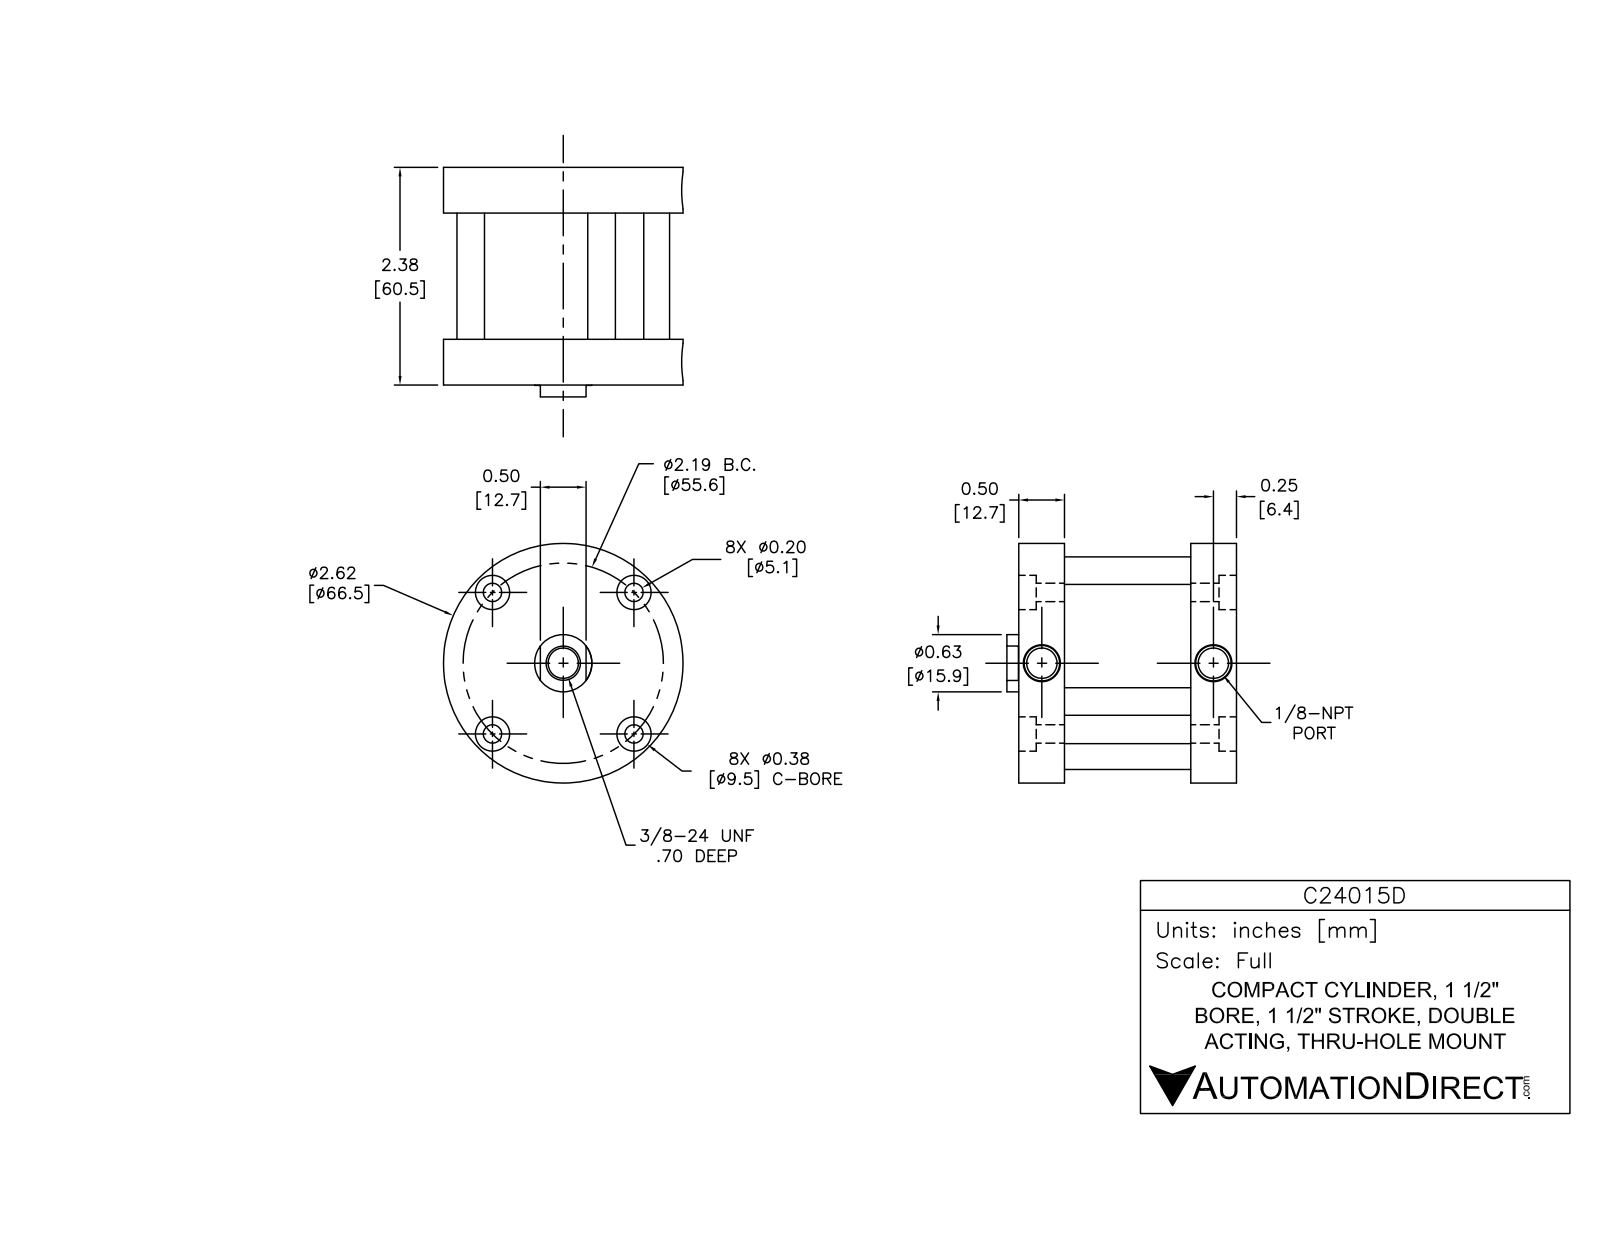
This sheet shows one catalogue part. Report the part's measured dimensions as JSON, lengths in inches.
{"part_name": "C24015D-FO1_BM_heads (2); C24015D-FO1_BM_rod; C24015D-FO1_BM_heads; C24015D-rod_part (+3 more)", "step_written_by": "SolidWorks 2014 (AUTOMOTIVE_DESIGN)", "units": "inches", "bodies": {"solids": 9, "faces": 165, "planar": 49, "cylindrical": 98, "other": 18}, "overall_size": [2.62, 2.62, 2.51], "volume_in3": 6.193, "surface_area_in2": 74.21, "round_holes": [[0.2, 4], [0.218, 4], [0.343, 4], [0.125, 2], [0.33, 1], [0.63, 1], [0.632, 1], [1.503, 1], [1.563, 1]], "round_bosses_or_shafts": [[0.4, 4], [2.62, 1]], "face_to_face_distances": [0.5, 1.88, 0.282, 2.098, 1.598, 0.218, 2.38, 1.38, 1.816, 0.598], "hole_center_spacings": [1.095, 1.549, 0.428, 1.217, 1.821, 2.148, 2.19, 2.191]}
